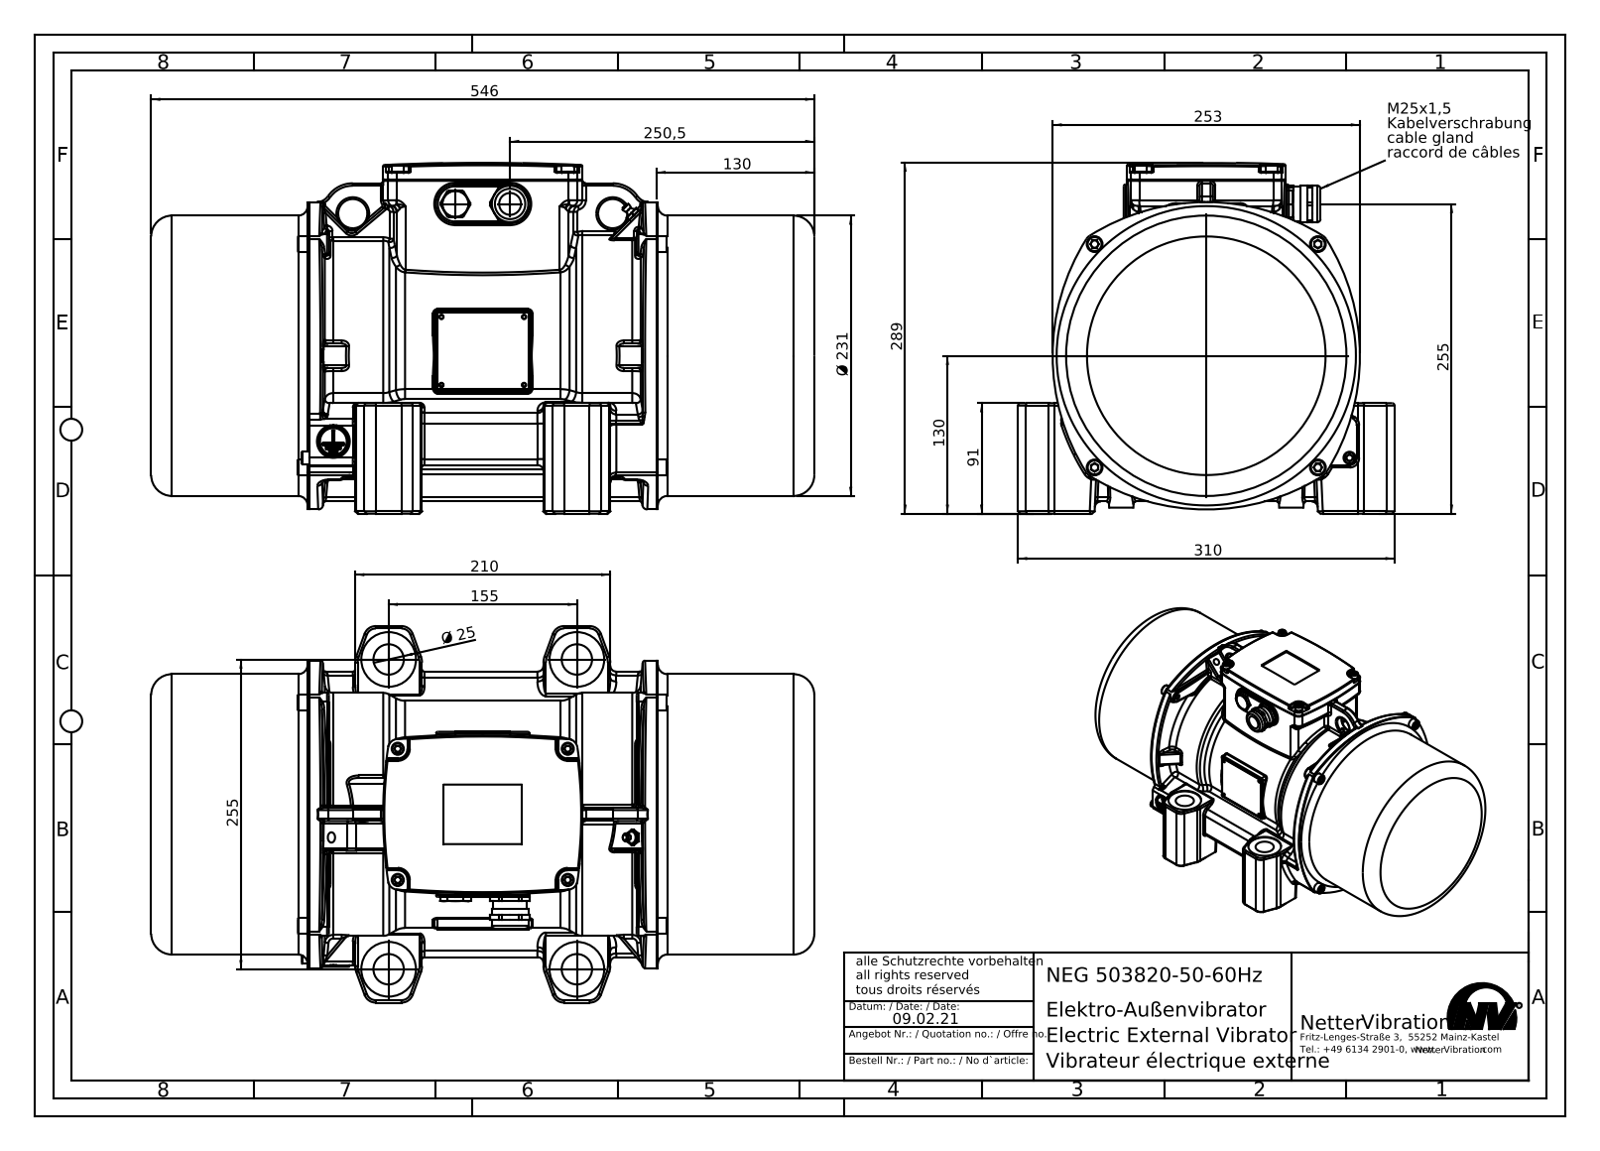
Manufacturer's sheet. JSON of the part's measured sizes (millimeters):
{"part_name": "NEG 503820-50-60Hz", "step_written_by": "SolidWorks 2015 (AUTOMOTIVE_DESIGN)", "units": "millimeters", "bodies": {"solids": 26, "faces": 3533, "planar": 1157, "cylindrical": 928, "other": 1448}, "overall_size": [546, 310, 288.82], "volume_mm3": 8313000, "surface_area_mm2": 1479000, "round_holes": [[5, 11], [3.2, 4], [3.5, 4], [6, 4], [6.5, 4], [6.75, 4], [9, 4], [10.25, 4], [25, 4], [45, 4], [8.5, 2], [24, 2]], "round_bosses_or_shafts": [[10, 5], [6, 5], [13, 4], [8, 4], [230.8, 1], [228, 1], [225, 1], [200, 1]], "partial_cylinders_radius": [[2, 80], [3, 80], [5, 56], [0.5, 46], [1.5, 32], [0.2, 21], [0.1, 16], [1.2, 16]], "face_to_face_distances": [1.2, 544.8, 416, 128.8, 109.8, 111, 435, 433.8, 543.6, 546], "hole_center_spacings": [166.17, 17.68, 26.5, 73.88, 164.8, 181.65, 233.5, 233.88]}
